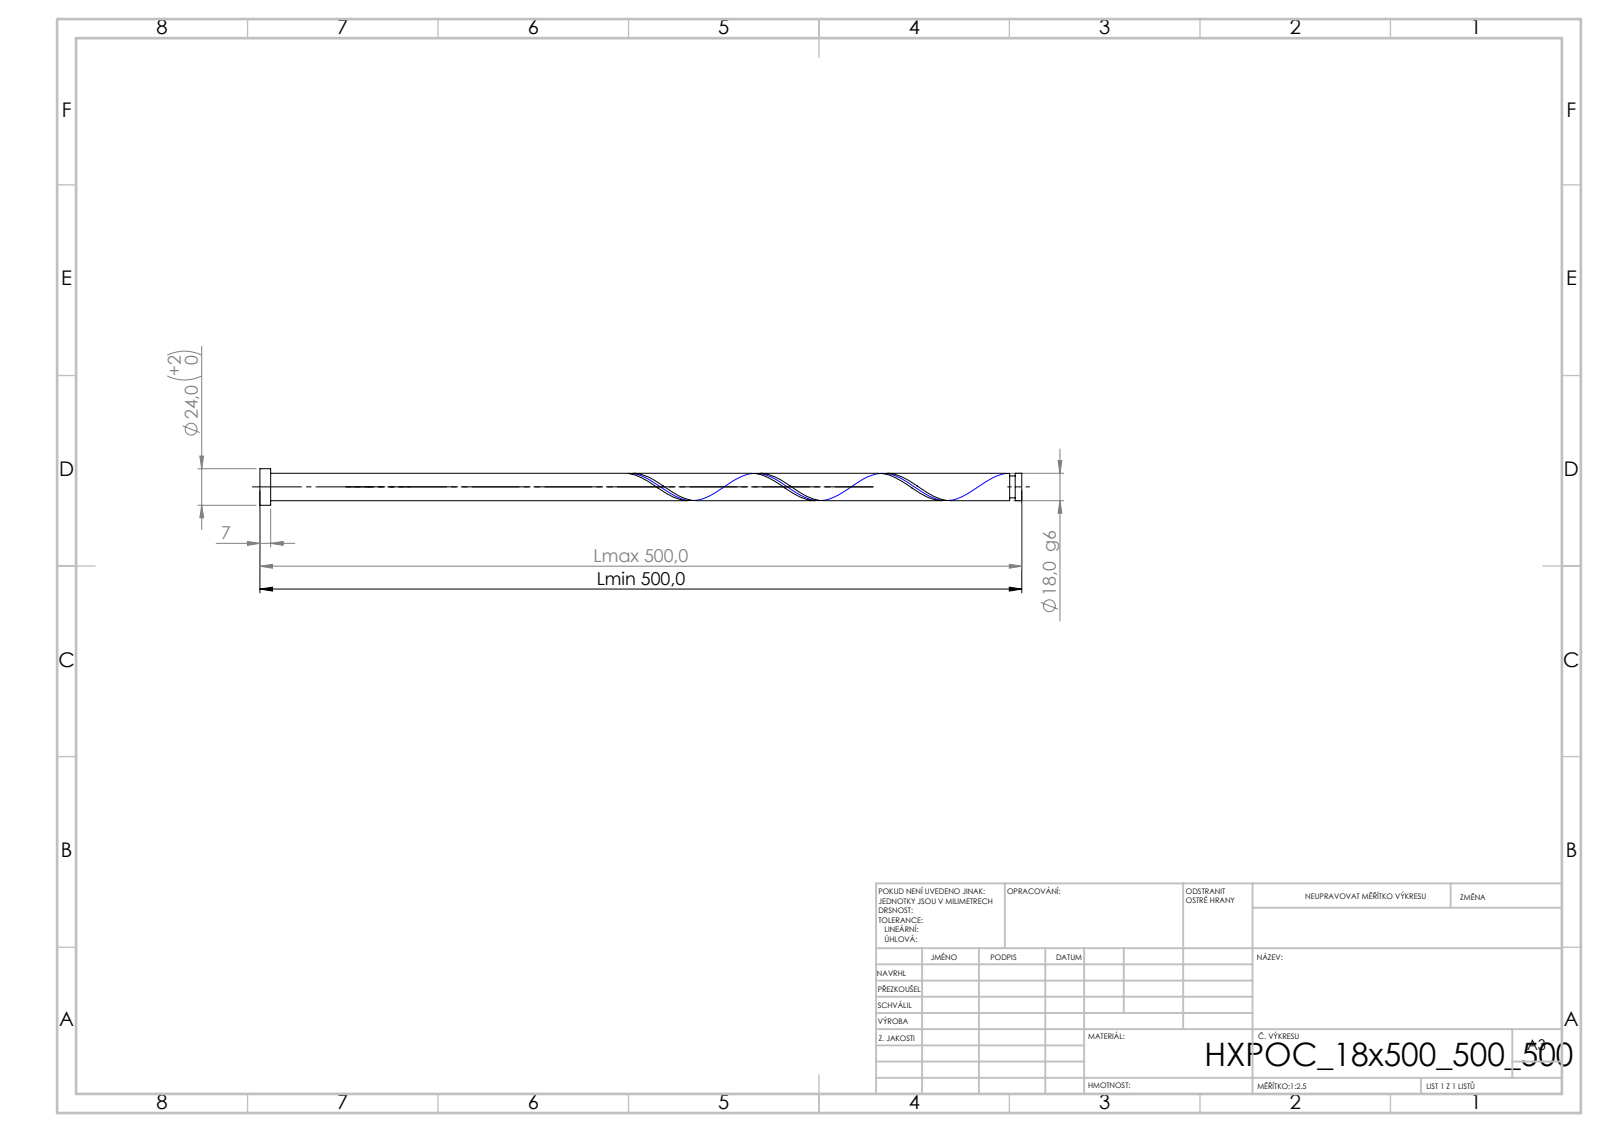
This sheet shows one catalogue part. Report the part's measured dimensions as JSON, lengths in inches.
{"step_written_by": "SolidWorks 2019 (CONFIG_CONTROL_DESIGN)", "units": "inches", "bodies": {"solids": 1, "faces": 21, "planar": 6, "cylindrical": 14, "other": 1}, "overall_size": [19.685, 0.945, 0.945], "volume_in3": 7.754, "surface_area_in2": 46.51, "round_bosses_or_shafts": [[0.945, 1], [0.709, 1], [0.567, 1]], "face_to_face_distances": [19.685, 0.276, 19.409, 19.514, 19.239, 0.171, 19.372, 19.097, 0.142, 0.313]}
